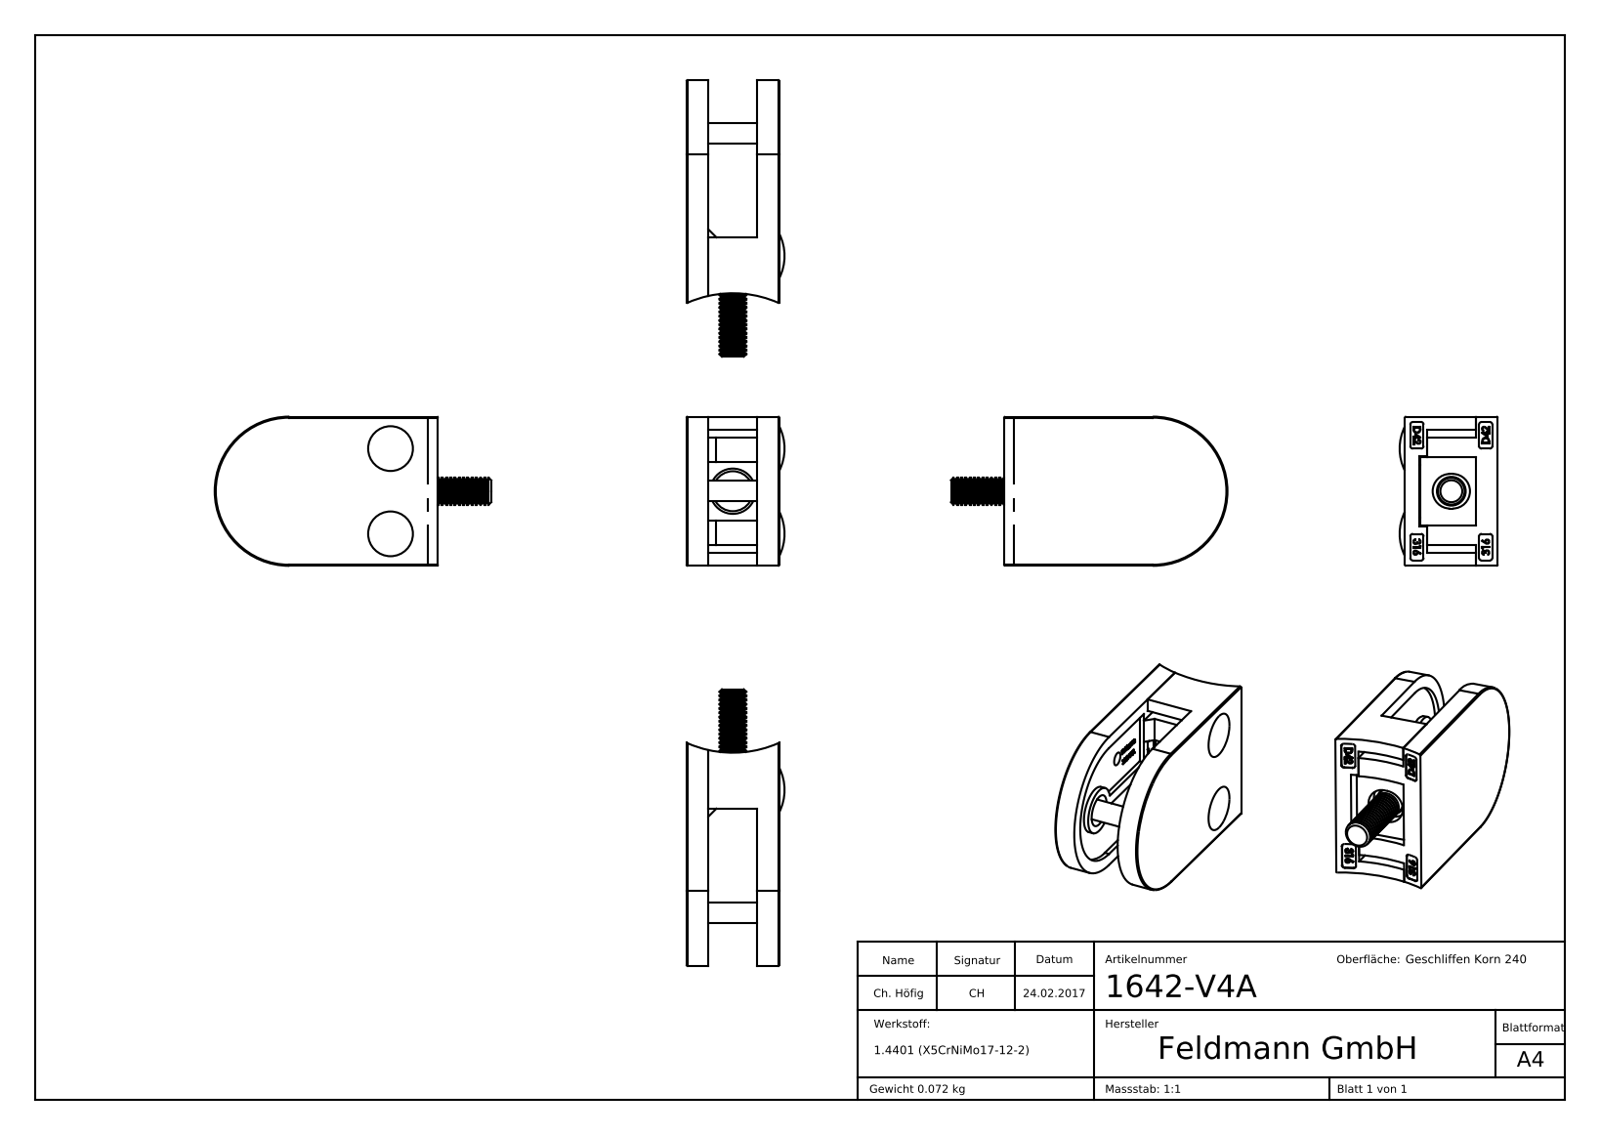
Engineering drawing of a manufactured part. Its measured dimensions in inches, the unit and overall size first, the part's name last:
Units: inches
Overall size (bounding box): 2.043 × 1.102 × 0.724
Round holes (diameter × count): ⌀0.039 ×2, ⌀0.098 ×2, ⌀0.13 ×2, ⌀0.163 ×2, ⌀0.323 ×2, ⌀0.154 ×1, ⌀0.236 ×1
Round bosses / shafts (diameter × count): ⌀0.301 ×2, ⌀0.157 ×2, ⌀0.098 ×2, ⌀0.346 ×1, ⌀0.335 ×1, ⌀0.197 ×1, ⌀0.152 ×1
Partial cylindrical surfaces — rounded edges, fillets, slot ends (radius × count): R0.02 ×20, R0.008 ×4, R0.128 ×2, R0.457 ×1, R0.551 ×1, R0.835 ×1, R0.839 ×1
Main face-to-face distances: 0.685, 0.161, 0.524, 0.126, 0.559, 0.035, 0.398, 0.433, 0.362, 0.098
Hole centre spacings: 0.433, 0.555, 0.788, 0.959, 0.496, 0.63
Volume: 0.596 in³ · Surface area: 13.97 in²
Bodies: 8 solids, 1391 faces (678 planar, 204 cylindrical, 509 other)
Part name (STEP PRODUCT): 16xx-XXX Teil1_1642-V4A; 16-Stift_16-Stift; socket head thin cap screw_din_DIN 7984 - M5 x 16 --- 16S; 16xx-XXX Teil2_1642-V4A (+3 more)
STEP written by: SolidWorks 2015 (CONFIG_CONTROL_DESIGN)
